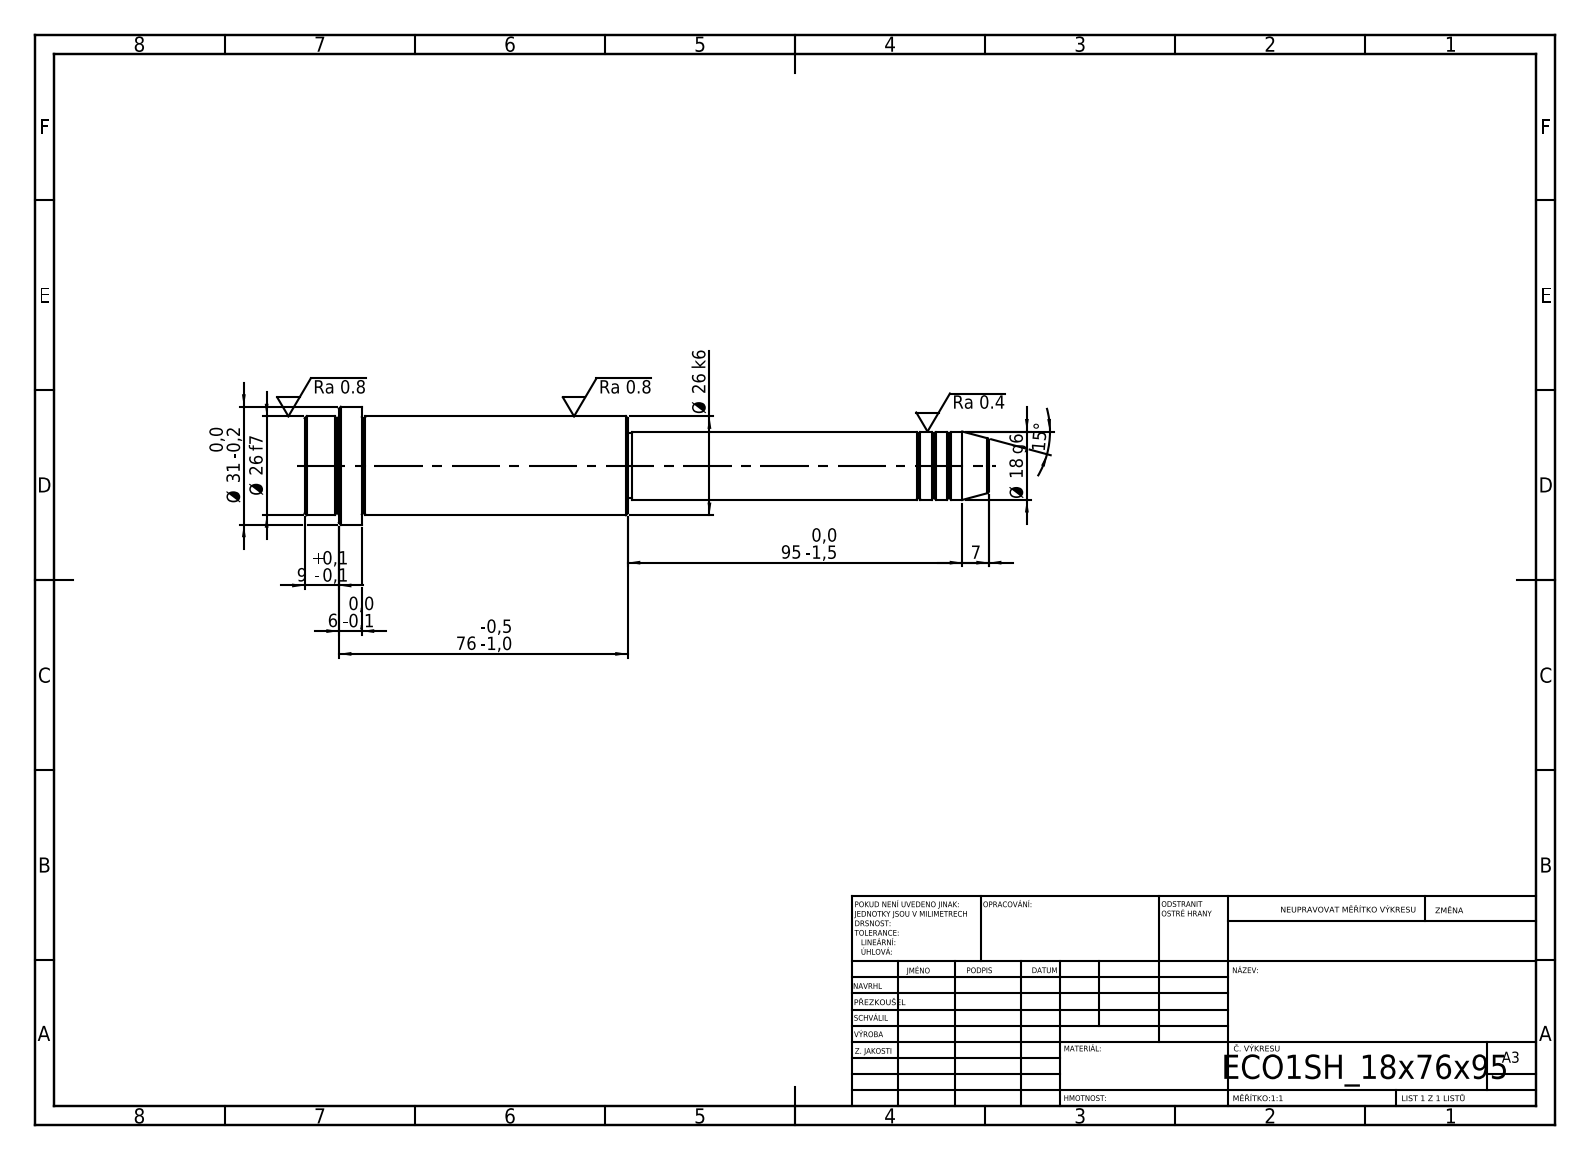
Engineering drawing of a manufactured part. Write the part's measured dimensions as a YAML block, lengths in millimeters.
step_written_by: "SolidWorks 2019 (CONFIG_CONTROL_DESIGN)"
units: millimeters
bodies: {solids: 1, faces: 52, planar: 6, cylindrical: 16, other: 30}
overall_size: [180, 31, 31]
volume: 70112
surface_area: 13939
round_bosses_or_shafts:
  - {diameter: 31, count: 1}
  - {diameter: 26, count: 1}
  - {diameter: 18, count: 1}
  - {diameter: 17, count: 1}
face_to_face_distances: [85, 70, 15, 76, 6, 9, 95, 165, 171, 180]
